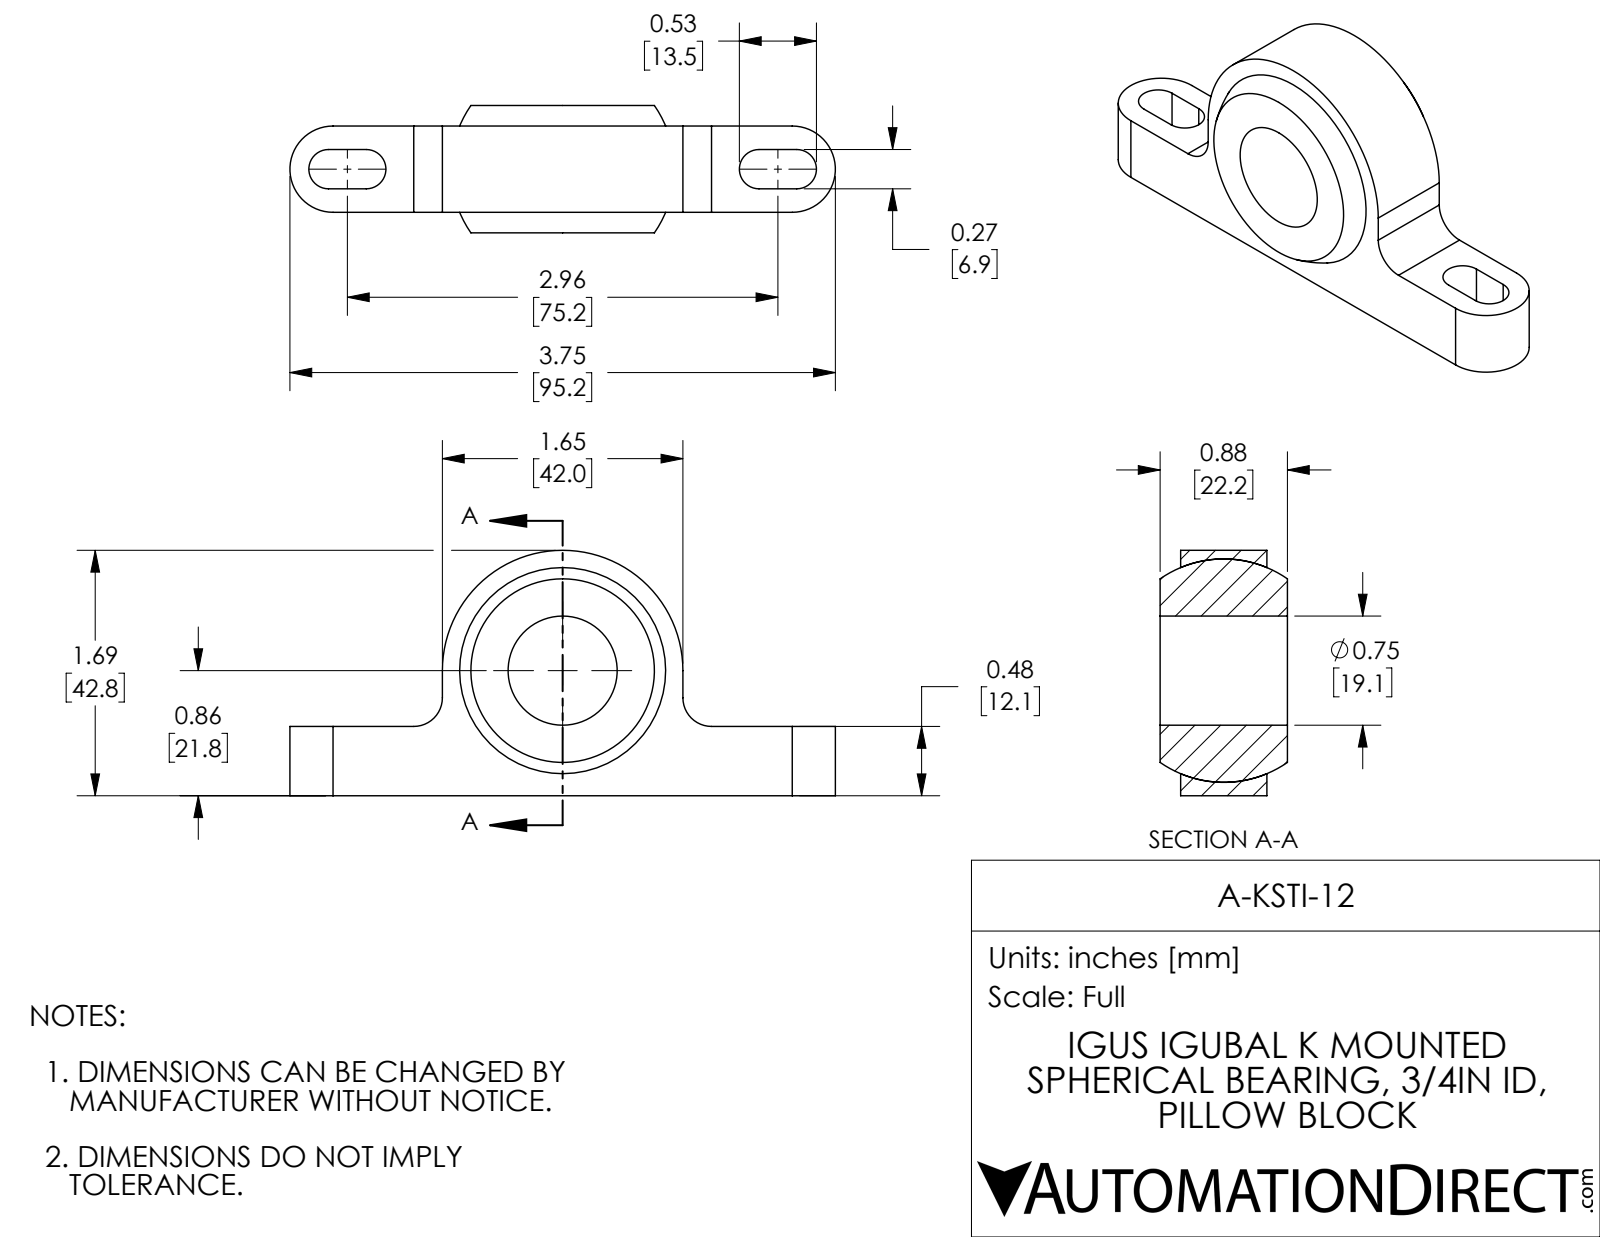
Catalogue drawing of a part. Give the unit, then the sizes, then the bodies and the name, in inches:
Units: inches
Overall size (bounding box): 3.75 × 1.687 × 0.875
Round holes (diameter × count): ⌀0.75 ×1
Partial cylindrical surfaces — rounded edges, fillets, slot ends (radius × count): R0.135 ×4, R0.197 ×2, R0.296 ×2, R0.827 ×1
Main face-to-face distances: 0.593, 0.141, 0.734, 0.875, 0.476, 0.302, 0.572, 0.161, 0.431, 0.27
Volume: 1.939 in³ · Surface area: 20.96 in²
Bodies: 2 solids, 31 faces (13 planar, 14 cylindrical, 4 other)
Part name (STEP PRODUCT): A-KSTI-12
STEP written by: SolidWorks 2017 (AUTOMOTIVE_DESIGN)
